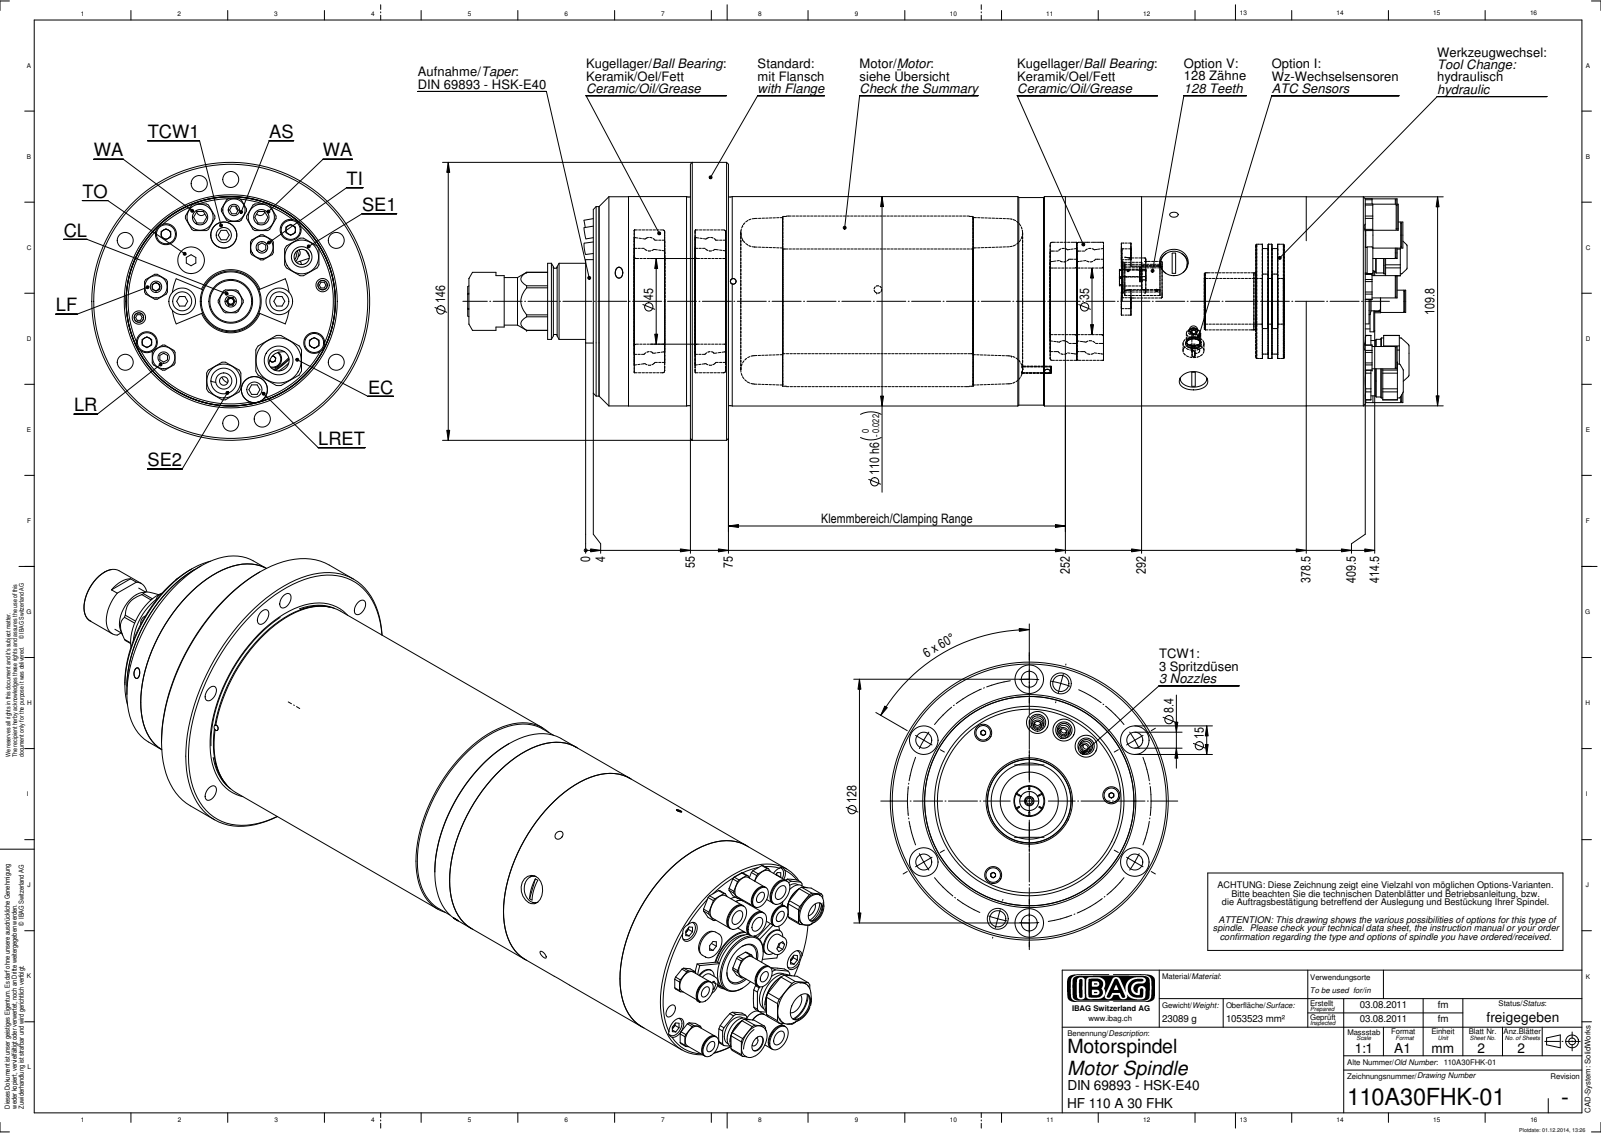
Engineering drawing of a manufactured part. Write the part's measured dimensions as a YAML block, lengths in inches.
part_name: "110A30FHK-01"
step_written_by: "SolidWorks 2012 (CONFIG_CONTROL_DESIGN)"
units: inches
bodies: {solids: 0, faces: 786, planar: 293, cylindrical: 338, other: 155}
overall_size: [19.467, 5.748, 5.748]
round_holes:
  - {diameter: 0.591, count: 9}
  - {diameter: 0.177, count: 7}
  - {diameter: 0.433, count: 7}
  - {diameter: 0.331, count: 6}
  - {diameter: 0.236, count: 5}
  - {diameter: 0.315, count: 5}
  - {diameter: 0.335, count: 3}
  - {diameter: 0.453, count: 3}
  - {diameter: 0.276, count: 2}
  - {diameter: 0.197, count: 1}
  - {diameter: 0.268, count: 1}
  - {diameter: 0.394, count: 1}
round_bosses_or_shafts:
  - {diameter: 0.461, count: 5}
  - {diameter: 0.551, count: 4}
  - {diameter: 0.539, count: 4}
  - {diameter: 0.301, count: 3}
  - {diameter: 0.236, count: 3}
  - {diameter: 0.701, count: 2}
  - {diameter: 0.661, count: 2}
  - {diameter: 0.614, count: 2}
partial_cylinders:
  - {radius: 0.26, count: 5}
  - {radius: 0.305, count: 2}
  - {radius: 0.39, count: 2}
  - {radius: 0.52, count: 1}
  - {radius: 1.22, count: 1}
face_to_face_distances: [15.236, 2.067, 13.169, 0.787, 0.728, 2.795, 15.965, 2.008, 1.28, 13.957]
hole_center_spacings: [2.52, 1.929, 4.364, 0.657, 0.967, 1.62, 1.634, 2.895]
